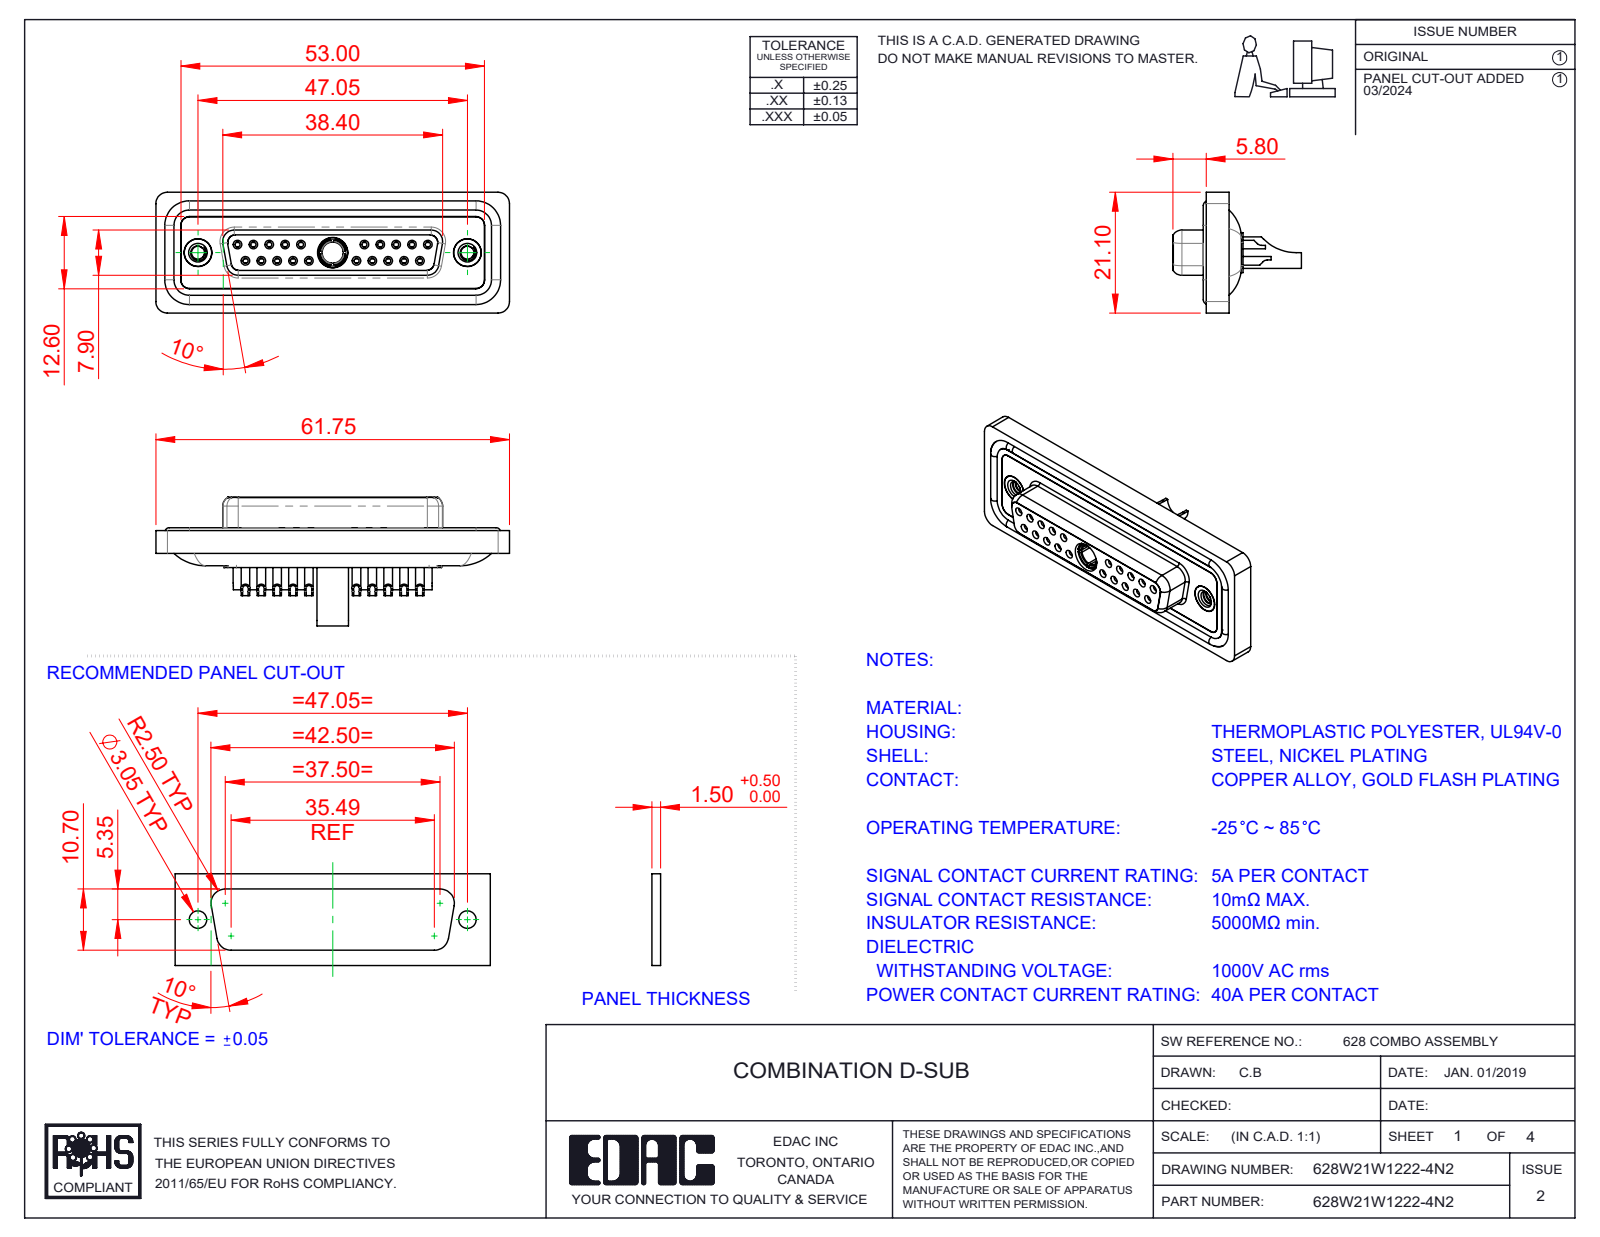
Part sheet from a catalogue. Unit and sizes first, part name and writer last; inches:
Units: inches
Overall size (bounding box): 2.431 × 0.884 × 0.831
Round holes (diameter × count): ⌀0.035 ×20, ⌀0.039 ×20, ⌀0.043 ×20, ⌀0.059 ×20, ⌀0.079 ×20, ⌀0.063 ×10, ⌀0.067 ×10, ⌀0.191 ×3, ⌀0.089 ×2, ⌀0.157 ×2, ⌀0.159 ×2, ⌀0.197 ×2
Round bosses / shafts (diameter × count): ⌀0.087 ×20, ⌀0.063 ×14, ⌀0.195 ×2, ⌀0.189 ×2, ⌀0.217 ×1, ⌀0.205 ×1, ⌀0.195 ×1, ⌀0.187 ×1
Partial cylindrical surfaces — rounded edges, fillets, slot ends (radius × count): R0.059 ×22, R0.079 ×18, R0.053 ×8, R0.063 ×8, R0.039 ×6, R0.01 ×4, R0.02 ×4, R0.024 ×4
Main face-to-face distances: 0.016, 0.071, 0.293, 0.222, 0.26, 0.02, 0.063, 0.278, 0.114, 0.043
Hole centre spacings: 0.124, 0.109, 0.218, 0.198, 0.327, 0.294, 0.654, 0.763
Volume: 0.516 in³ · Surface area: 22.25 in²
Bodies: 29 solids, 1563 faces (476 planar, 632 cylindrical, 455 other)
Part name (STEP PRODUCT): 628Combo Threaded Rivet_2; 628Combo Waterproof Housing_25 Contacts; 628Combo Shell Front_25 Contacts; 628W21W1222-4N2 (+5 more)
STEP written by: SolidWorks 2023 (CONFIG_CONTROL_DESIGN)
